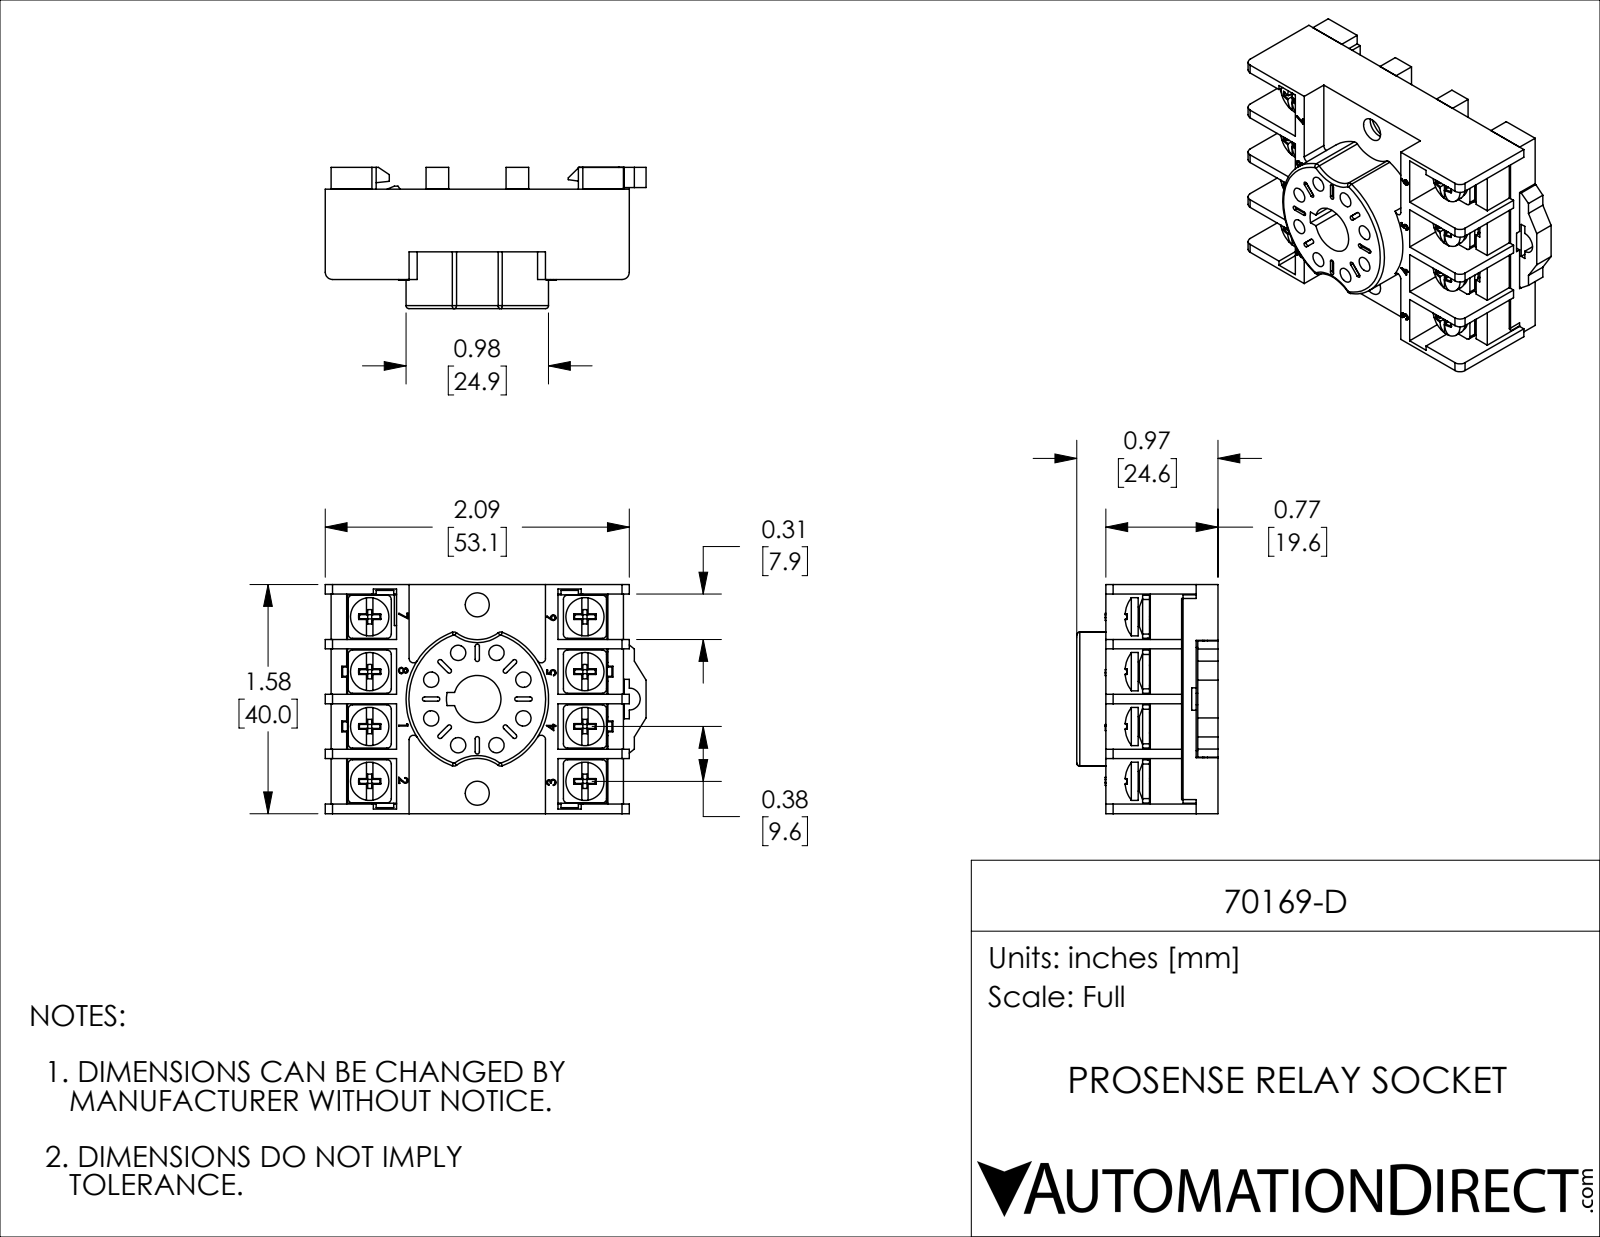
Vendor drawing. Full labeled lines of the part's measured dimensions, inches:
Part name (STEP PRODUCT): 70169-D
STEP written by: SolidWorks 2019 (AUTOMOTIVE_DESIGN)
Units: inches
Bodies: 19 solids, 1205 faces (816 planar, 182 cylindrical, 207 other)
Overall size (bounding box): 2.205 × 1.575 × 0.971
Volume: 1.571 in³ · Surface area: 35.14 in²
Round holes (diameter × count): ⌀0.105 ×8, ⌀0.138 ×8, ⌀0.18 ×8, ⌀0.165 ×2, ⌀0.325 ×1
Round bosses / shafts (diameter × count): ⌀0.263 ×8, ⌀0.134 ×8
Partial cylindrical surfaces — rounded edges, fillets, slot ends (radius × count): R0.03 ×40, R0.015 ×16, R0.02 ×3, R0.01 ×2, R0.05 ×2, R0.09 ×2, R0.15 ×2, R0.24 ×2
Main face-to-face distances: 0.29, 0.377, 0.075, 0.365, 0.066, 1.509, 0.065, 0.53, 1.575, 0.337
Hole centre spacings: 1.528, 1.48, 0.377, 1.661, 0.427, 0.605, 0.622, 0.657
